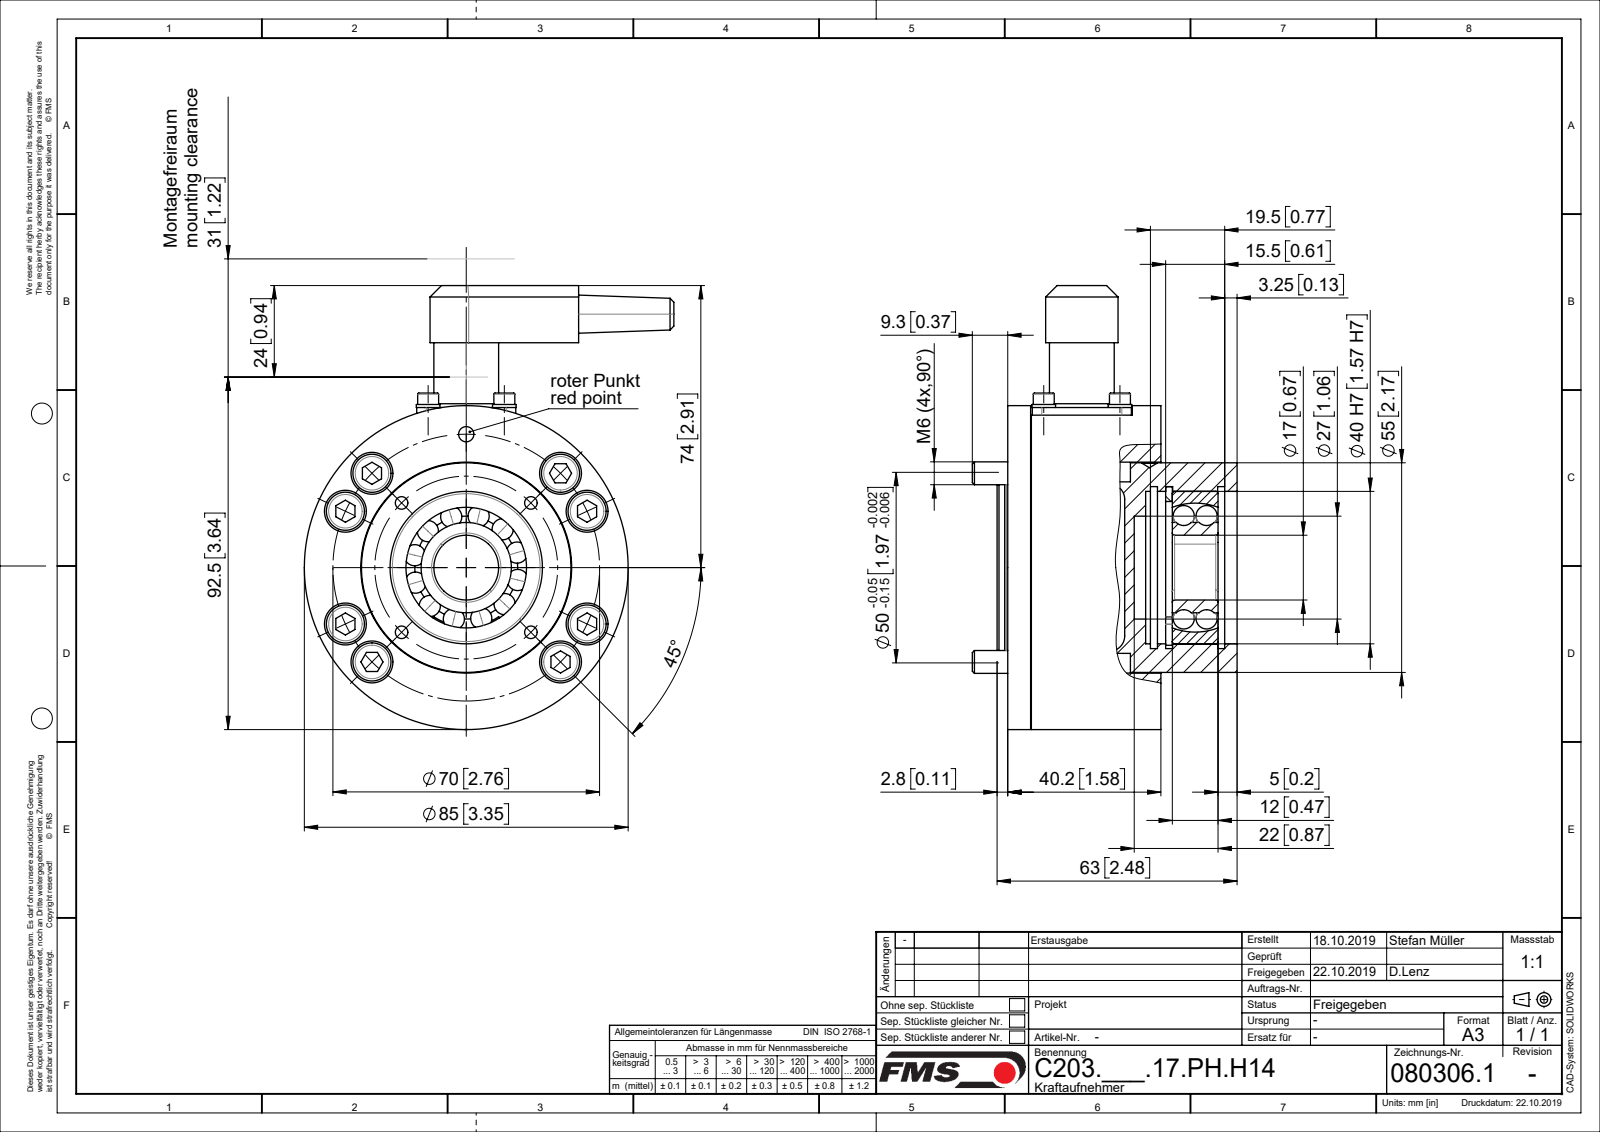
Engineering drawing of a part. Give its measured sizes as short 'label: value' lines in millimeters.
name: C0803061; C0709071; C0704203; C0709072 (+8 more)
written by: Mechanical Desktop 2007 (CONFIG_CONTROL_DESIGN)
unit: mm
bodies: 27 solids, 544 faces (191 planar, 254 cylindrical, 99 other)
size: 116.5 × 97 × 71.33
volume: 252 388 mm³; area: 86 240 mm²
holes: 8× ⌀6.5, 8× ⌀11, 5× ⌀2, 4× ⌀2.6, 4× ⌀3.2, 4× ⌀3.42, 4× ⌀5.15, 4× ⌀7, 1× ⌀4, 1× ⌀10.68, 1× ⌀12, 1× ⌀15
bosses: 8× ⌀10, 8× ⌀6, 5× ⌀1.5, 4× ⌀6.2, 4× ⌀5.5, 4× ⌀5, 4× ⌀3, 1× ⌀85
rounds: 4× R2.5, 2× R5, 1× R9.5
face distances: 6, 3, 34, 40, 43, 15, 4, 9, 24.5, 30.5
hole spacings: 35, 42.44, 20, 11, 12.16, 14.14, 14.91, 24
